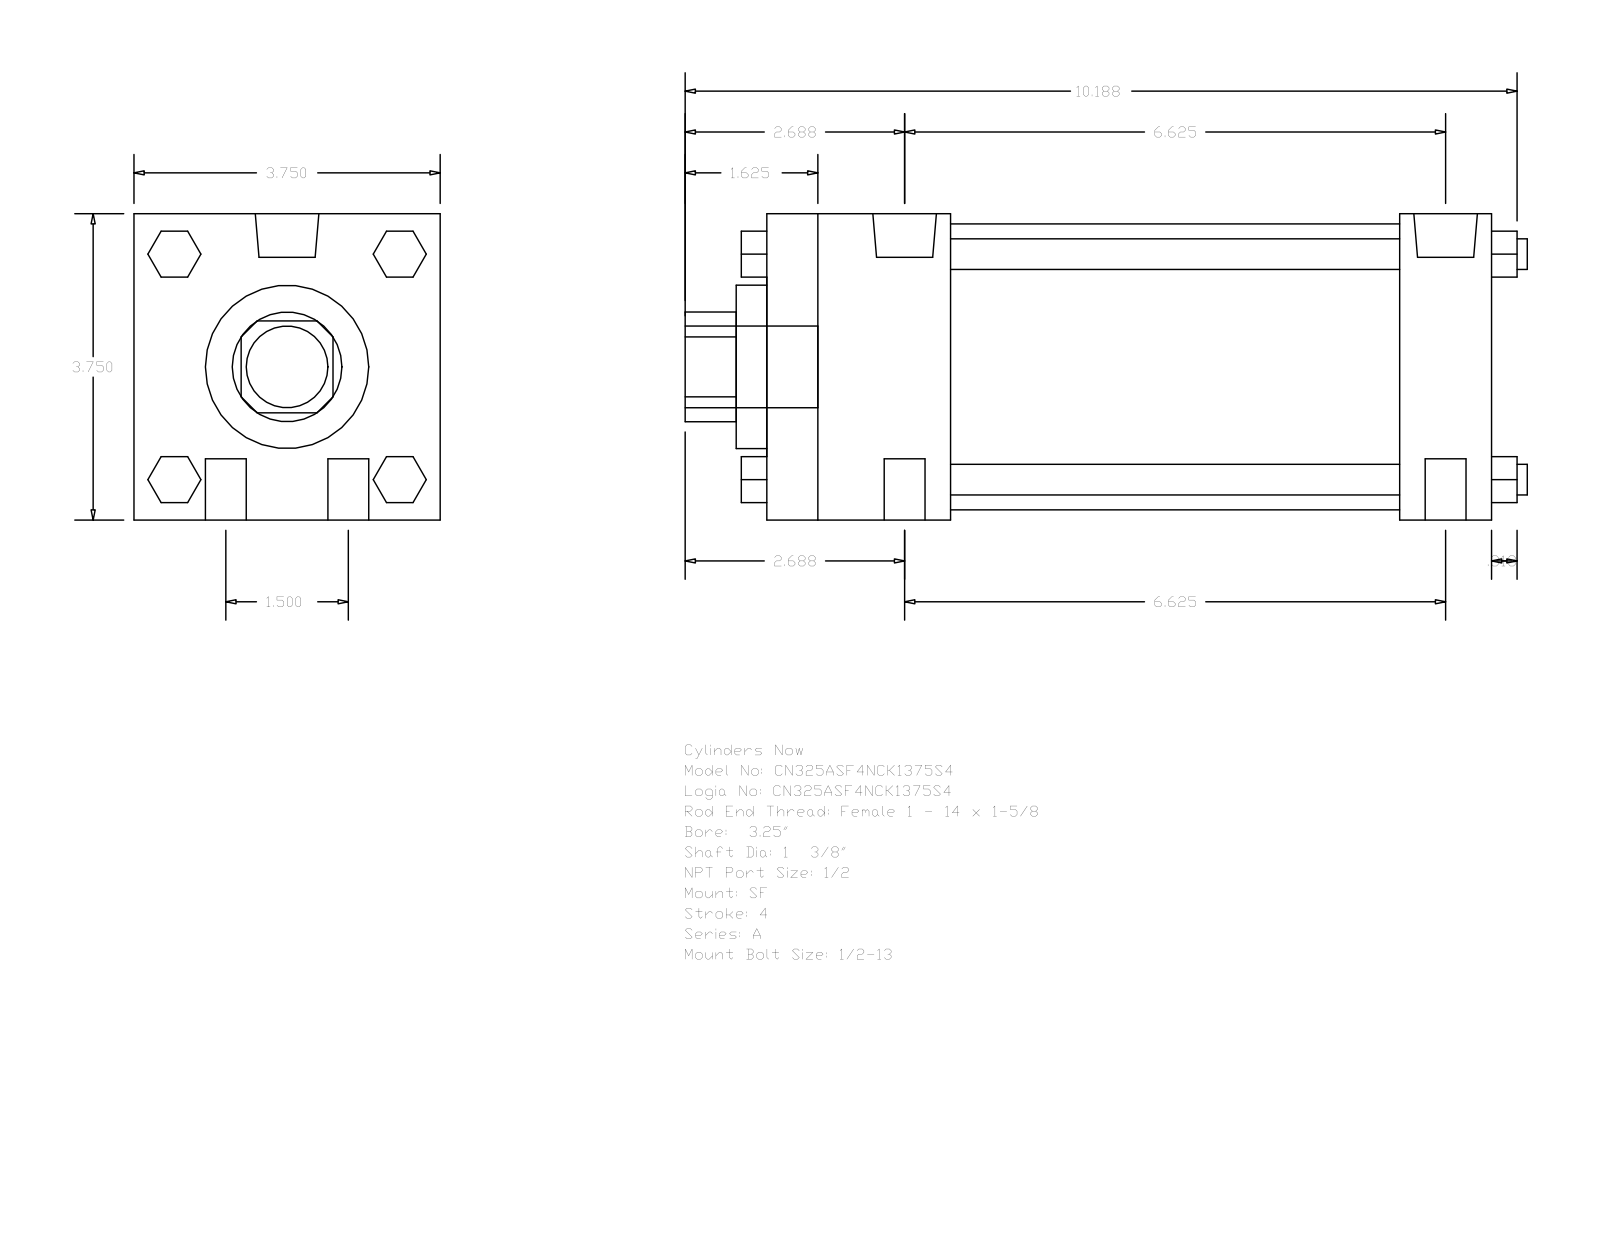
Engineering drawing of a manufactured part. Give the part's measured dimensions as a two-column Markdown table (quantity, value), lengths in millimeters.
| quantity | value |
| --- | --- |
| part name | A_SF__0325_1.375 |
| STEP written by | GSSL Pune (CONFIG_CONTROL_DESIGN) |
| units | millimeters |
| bodies | 0 solids, 124 faces (94 planar, 30 cylindrical, 0 other) |
| overall size | 261.94 × 95.25 × 95.25 |
| round holes (diameter × count) | 34.92 × 1, 50.8 × 1, 88.9 × 1 |
| round bosses / shafts (diameter × count) | 12.7 × 4, 9.53 × 4, 19.77 × 2, 8.73 × 2, 25.4 × 1 |
| partial cylindrical surfaces (radius × count) | 17.06 × 1 |
| main face-to-face distances | 95.24, 225.42, 28.57, 196.85, 57.15, 139.7, 168.27, 9.52, 66.67, 206.37 |
